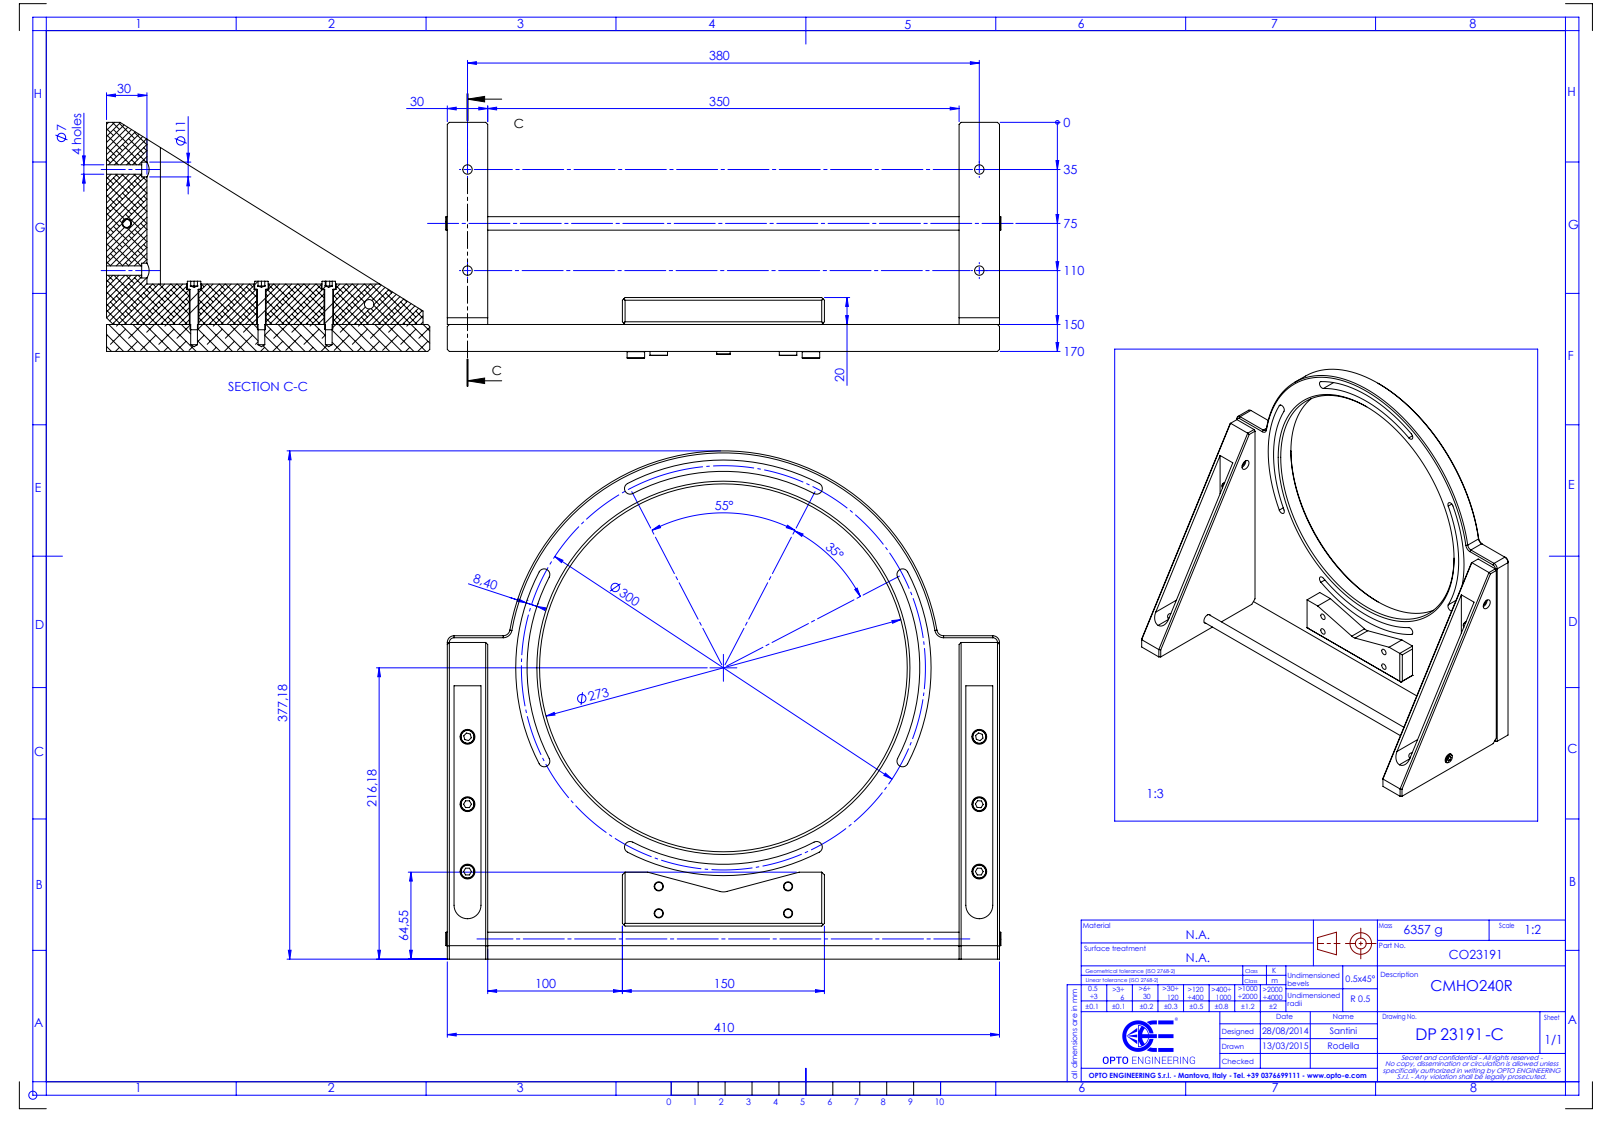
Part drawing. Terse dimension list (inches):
name: DP23191_CMHO240R
written by: SolidWorks 2021 (CONFIG_CONTROL_DESIGN)
unit: in
bodies: 0 solids, 281 faces (127 planar, 112 cylindrical, 42 other)
size: 16.22 × 14.85 × 6.89
holes: 5× ⌀0.276, 5× ⌀0.433, 4× ⌀0.268, 4× ⌀0.591, 1× ⌀10.748
bosses: 8× ⌀0.512, 4× ⌀0.394
rounds: 8× R0.165, 4× R0.197, 3× R0.394, 1× R5.74, 1× R6.071, 1× R6.339
face distances: 0.787, 14.961, 1.181, 0.197, 0.984, 16.142, 13.78, 15.157, 15.945, 14.764
hole spacings: 0.787, 1.904, 1.969, 2.953, 3.78, 3.861, 6.659, 7.417
